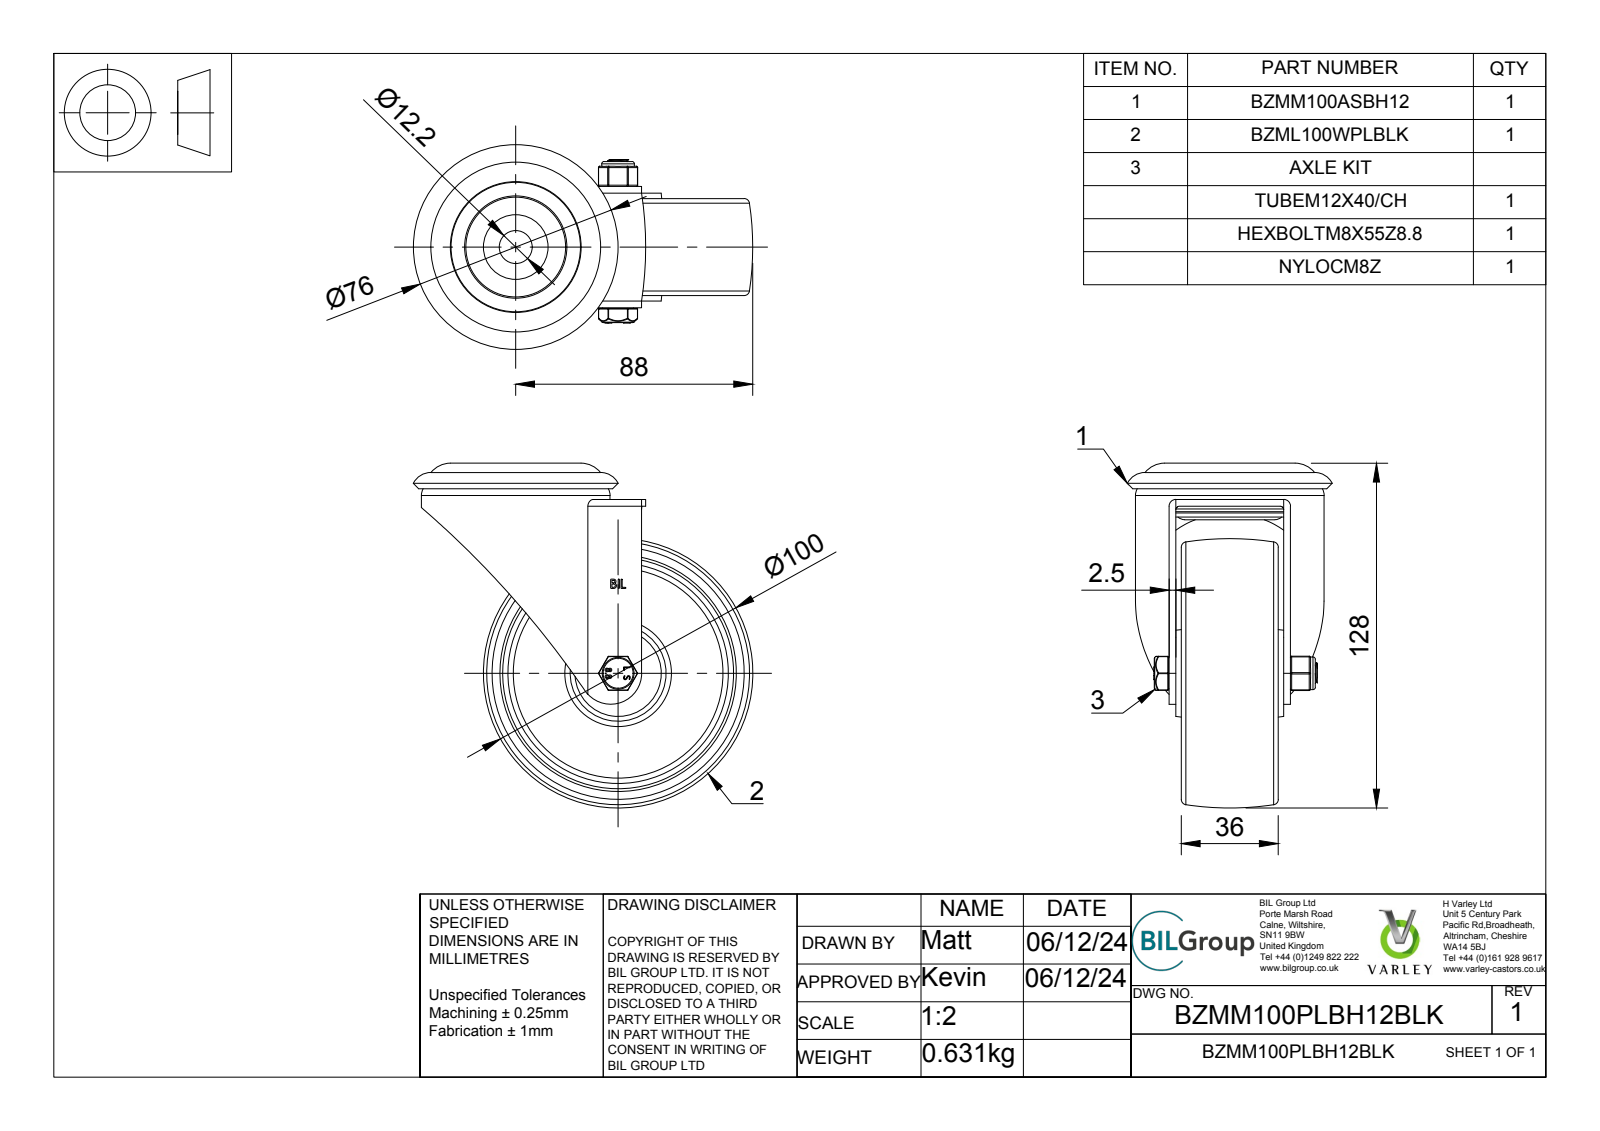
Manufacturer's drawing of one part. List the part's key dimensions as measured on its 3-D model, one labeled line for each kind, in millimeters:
Part name (STEP PRODUCT): BZMM100PLBH12BLK v3; BZMM100ASBH12 v1; ZINC PLATED PRESSED STEEL HEAD; ZINC PLATED, PRESSED STEEL FORKS (+8 more)
STEP written by: Autodesk Translation Framework v13.20.0.188 (AP242_MANAGED_MODEL_BASED_3D_ENGINEERING_MIM_LF)
Units: millimetres
Bodies: 7 solids, 335 faces (108 planar, 122 cylindrical, 105 other)
Overall size (bounding box): 128 × 126 × 76
Volume: 199 332 mm³ · Surface area: 85 810 mm²
Round holes (diameter × count): ⌀0.66 ×2, ⌀12.2 ×2, ⌀8 ×1, ⌀8.2 ×1, ⌀8.4 ×1, ⌀8.6 ×1, ⌀65 ×1, ⌀72 ×1
Round bosses / shafts (diameter × count): ⌀70 ×1, ⌀49.5 ×1, ⌀38 ×1, ⌀24 ×1, ⌀21.31 ×1, ⌀12.1 ×1, ⌀11.9 ×1, ⌀11.5 ×1
Partial cylindrical surfaces — rounded edges, fillets, slot ends (radius × count): R0.5 ×18, R0.25 ×12, R0.33 ×4, R0.64 ×4, R1.25 ×4, R0.63 ×2, R0.64 ×2, R2.5 ×2
Main face-to-face distances: 2.5, 17, 23, 6, 25.5, 19.5, 42.5, 40, 4.5, 2
Hole centre spacings: 3.22, 2.49
